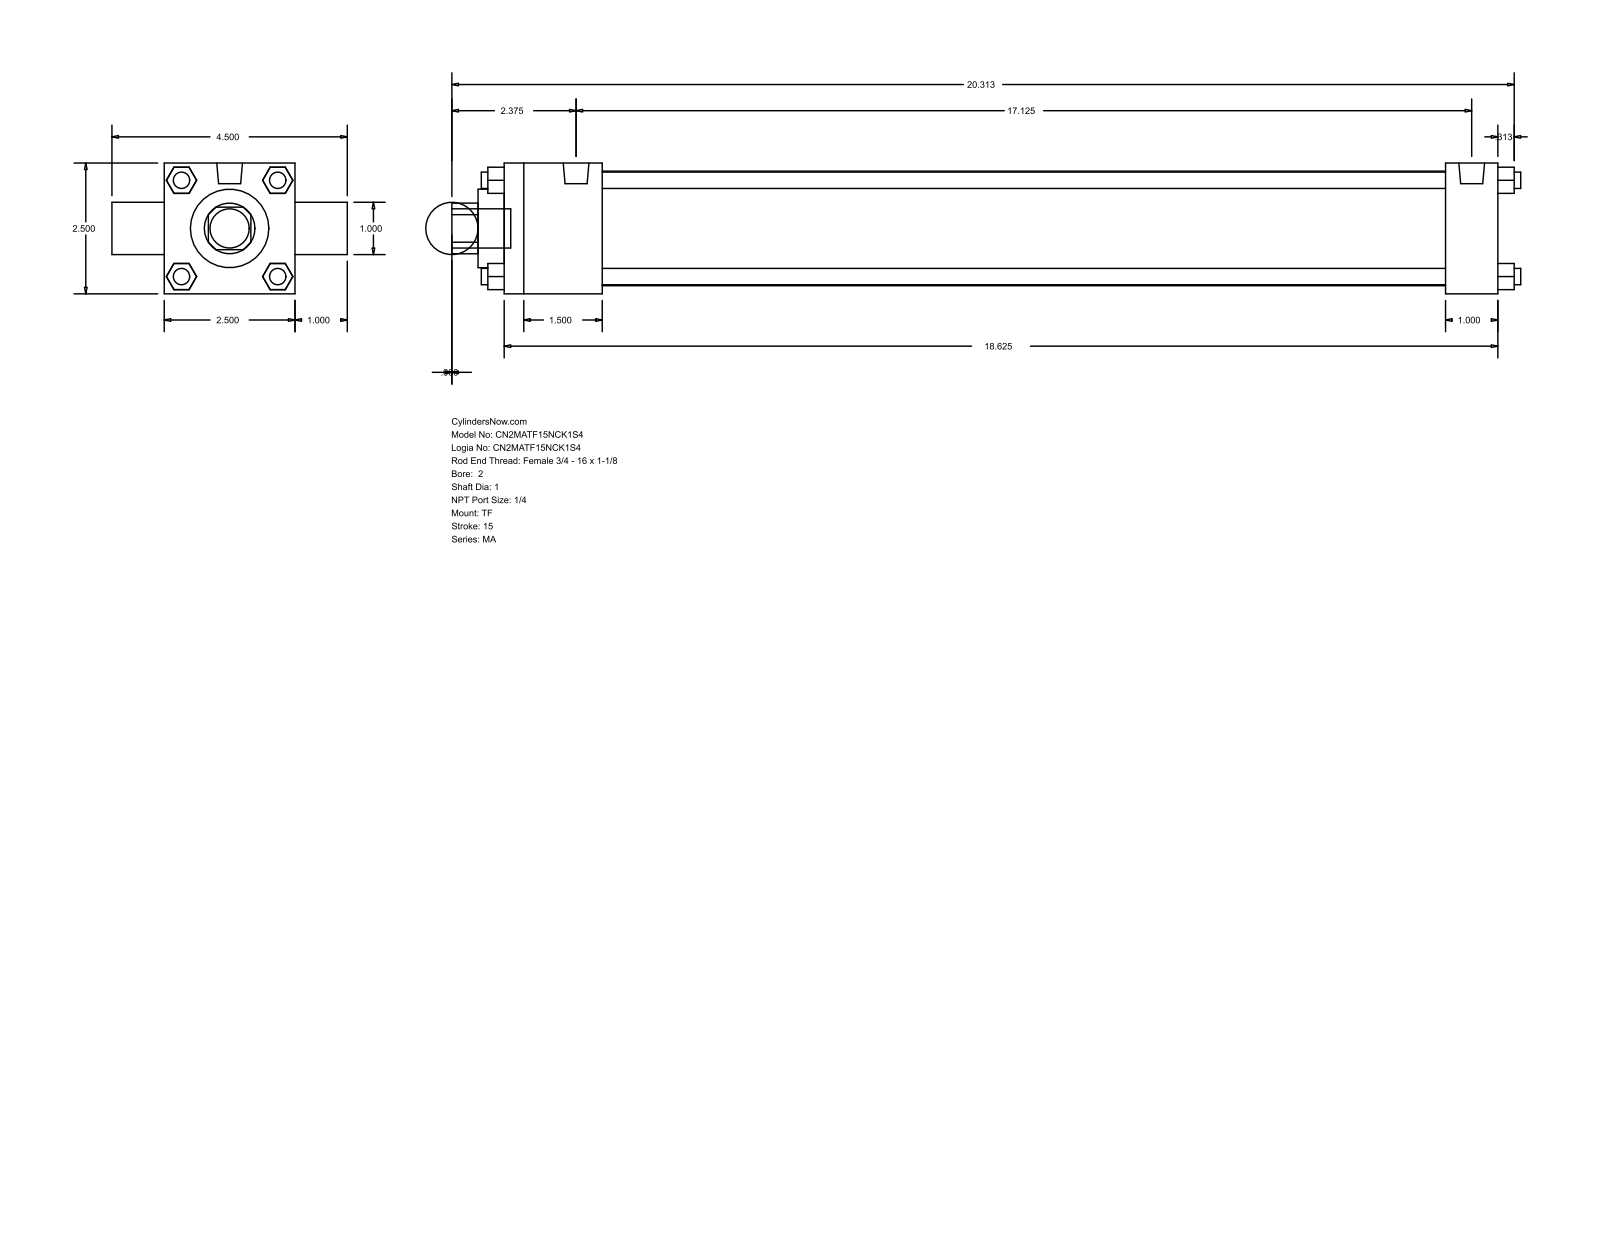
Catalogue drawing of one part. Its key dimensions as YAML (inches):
part_name: "MA_TF__0200_1"
step_written_by: "GSSL Pune (CONFIG_CONTROL_DESIGN)"
units: inches
bodies: {solids: 0, faces: 120, planar: 92, cylindrical: 28, other: 0}
overall_size: [20.437, 4.5, 2.5]
round_holes:
  - {diameter: 1, count: 2}
  - {diameter: 1.5, count: 1}
  - {diameter: 2.19, count: 1}
round_bosses_or_shafts:
  - {diameter: 0.313, count: 7}
  - {diameter: 0.492, count: 2}
  - {diameter: 0.75, count: 1}
partial_cylinders:
  - {radius: 0.484, count: 1}
face_to_face_distances: [2.5, 1, 19, 0.5, 1.875, 18, 16.125, 17.125, 3.5, 0.92]
